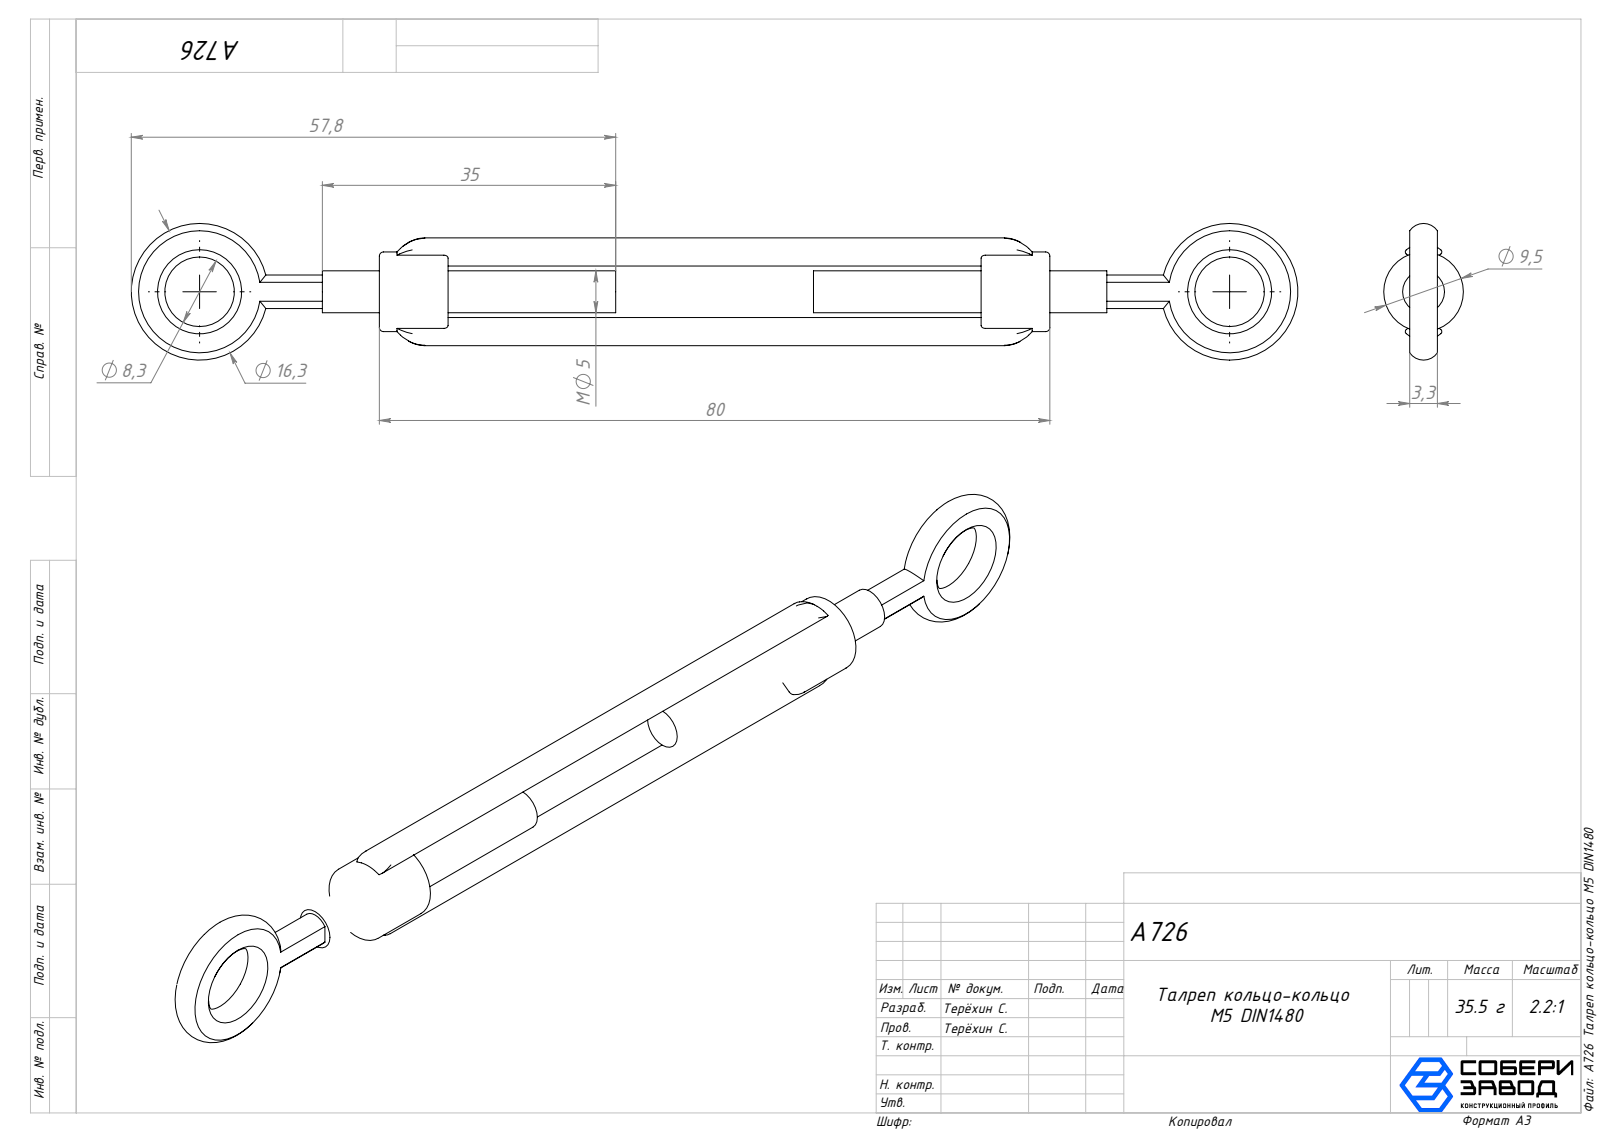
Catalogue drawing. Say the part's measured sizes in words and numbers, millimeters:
The part is named "Талреп основание_00; Сборка2; A726 Талреп кольцо-кольцо М5 DIN1480_00; Талреп кольцо_00". Its 3-D file was written by "SolidWorks 2025 (AUTOMOTIVE_DESIGN)". It is 3 solids with 84 faces: 20 planar, 26 cylindrical and 38 other. Overall it measures 139.2 by 16.3 by 9.5 millimeters. Its volume is 4 526 cubic millimeters and its surface area 4 641 square millimeters. Round holes: 1 of diameter 4. Round bosses or shafts: 1 of diameter 9.5, 1 of diameter 5. Partial cylindrical surfaces (rounded edges, fillets, slot ends): 8 of radius 0.3. The main face-to-face distances are 2.83, 7.67, 10.5, 3.3, 2.82, 4.85, 7.68, 4.84, 8.2, 71.8.
